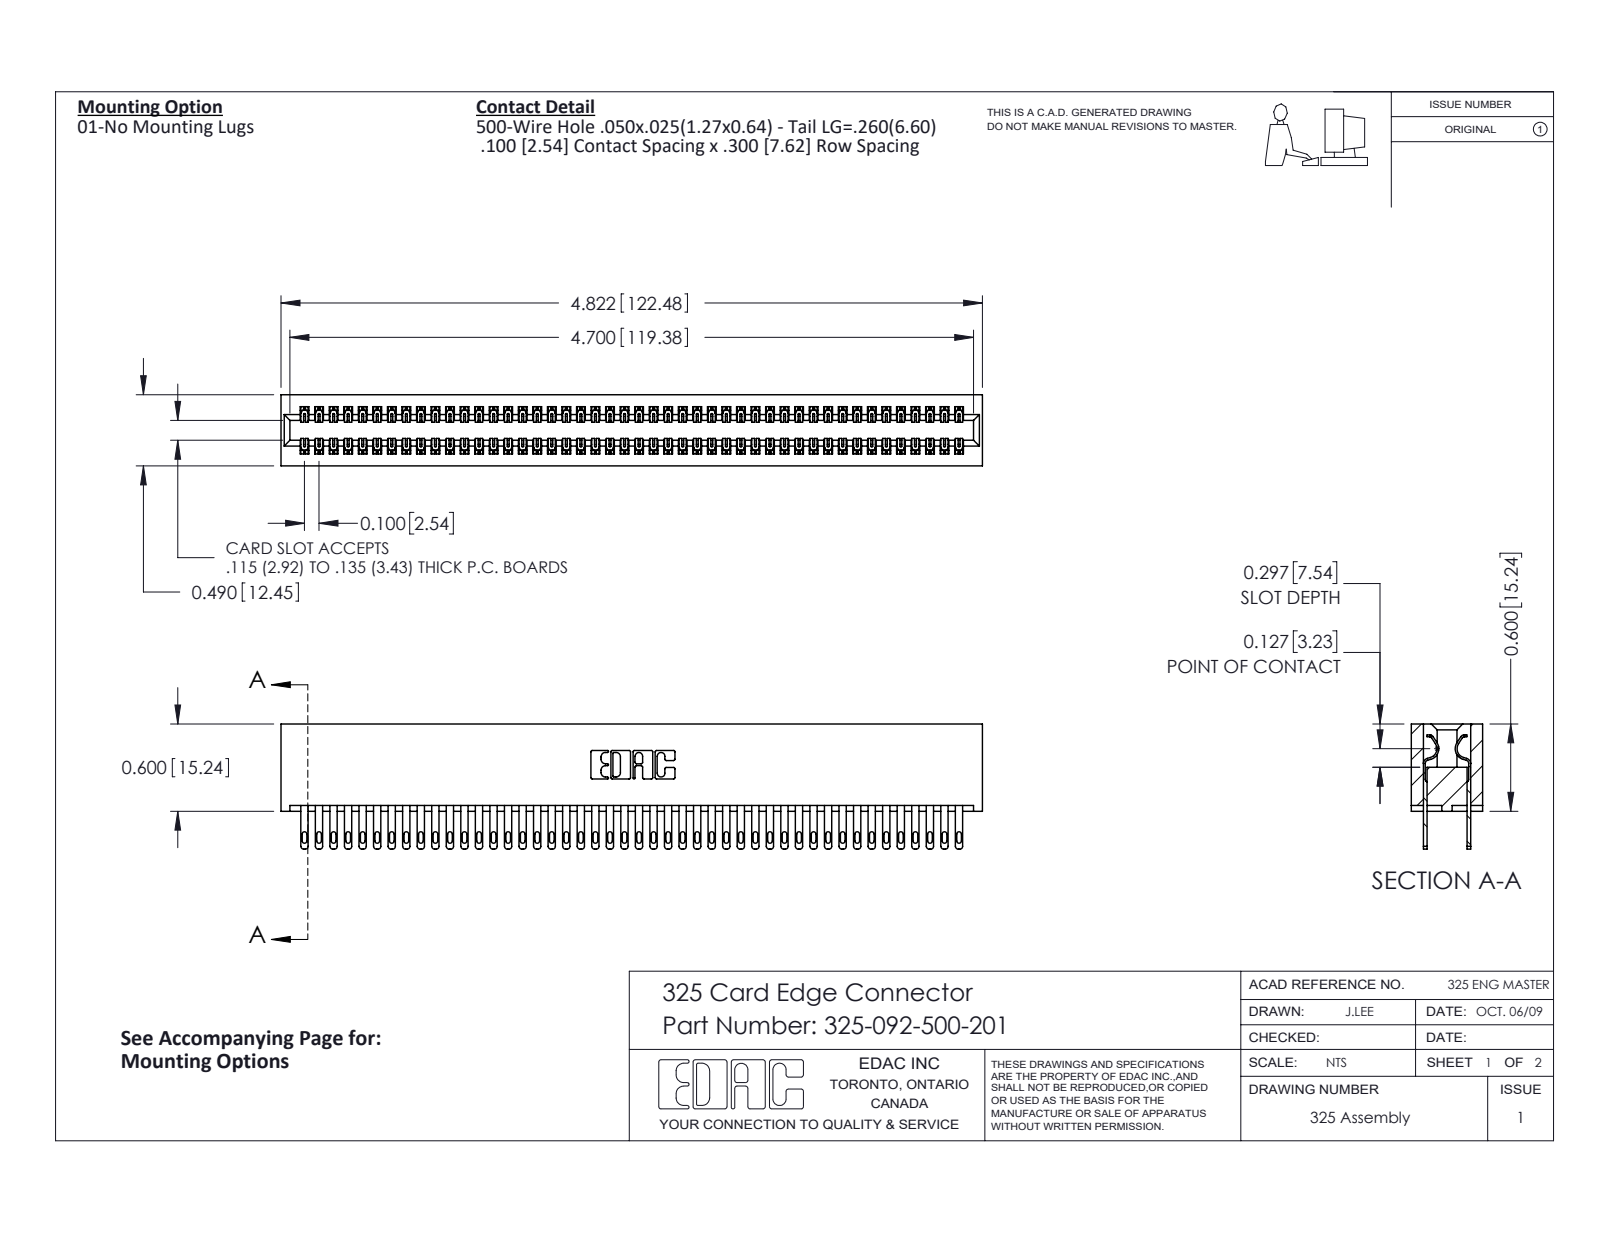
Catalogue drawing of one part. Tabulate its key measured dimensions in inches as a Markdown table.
| quantity | value |
| --- | --- |
| part name | 325 Part_Lugless; 325-092-500-201; 325-292-001_325-293-100 |
| STEP written by | SolidWorks 2016 (CONFIG_CONTROL_DESIGN) |
| units | inches |
| bodies | 93 solids, 4522 faces (2826 planar, 1696 cylindrical, 0 other) |
| overall size | 4.822 × 0.86 × 0.49 |
| volume | 1.021 in³ |
| surface area | 34.06 in² |
| partial cylindrical surfaces (radius × count) | 0.006 × 138, 0.016 × 92, 0.02 × 92, 0.01 × 22, 0.007 × 6, 0.031 × 6, 0.026 × 3, 0.014 × 2 |
| main face-to-face distances | 0.083, 0.407, 0.3, 0.107, 0.383, 0.025, 0.325, 0.49, 0.275, 0.56 |
